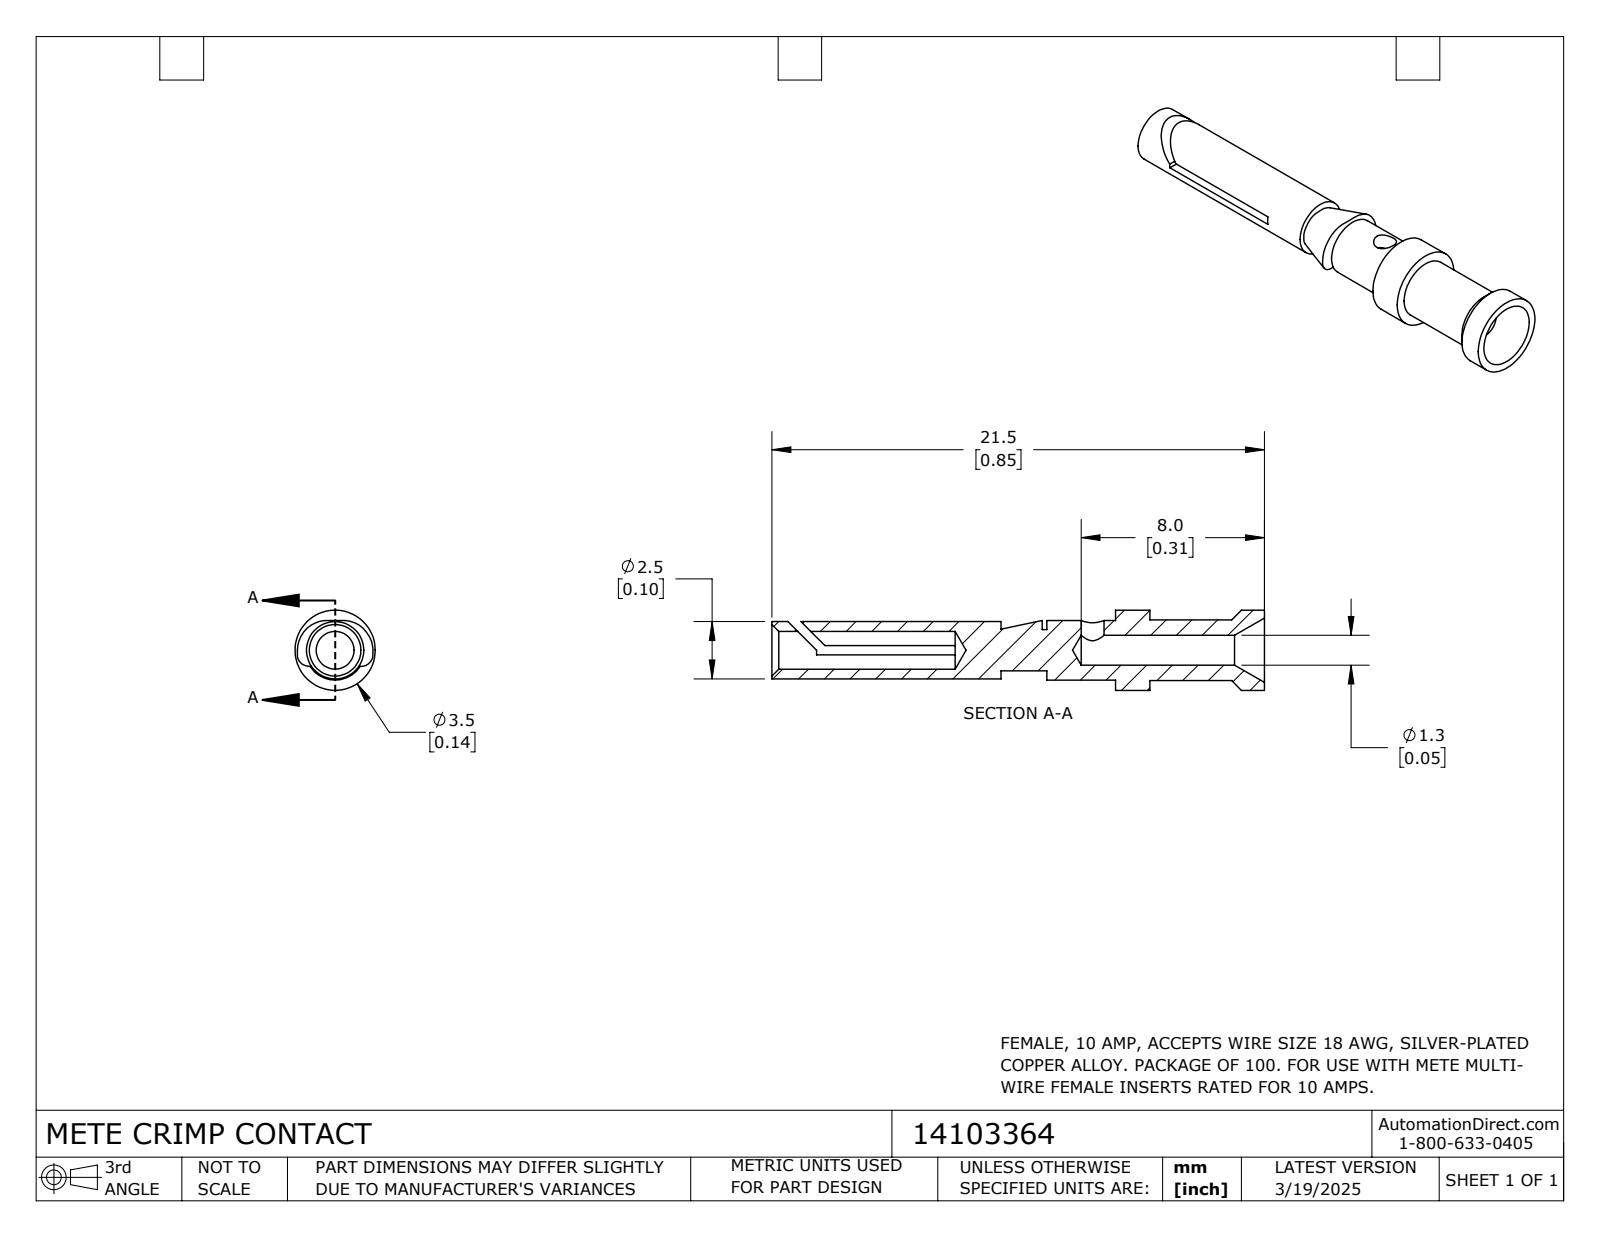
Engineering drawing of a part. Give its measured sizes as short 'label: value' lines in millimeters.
name: 14103364
written by: SolidWorks 2024 (CONFIG_CONTROL_DESIGN)
unit: mm
bodies: 1 solid, 48 faces (17 planar, 20 cylindrical, 11 other)
size: 21.5 × 3.5 × 3.5
volume: 86 mm³; area: 288 mm²
holes: 1× ⌀1, 1× ⌀1.3, 1× ⌀1.65
bosses: 1× ⌀3.5, 1× ⌀2.65, 1× ⌀2.6, 1× ⌀2.5, 1× ⌀1.8
face distances: 0.4, 5, 6.5, 1.5, 9.7, 4.7, 3.2, 9.5, 4.5, 3
